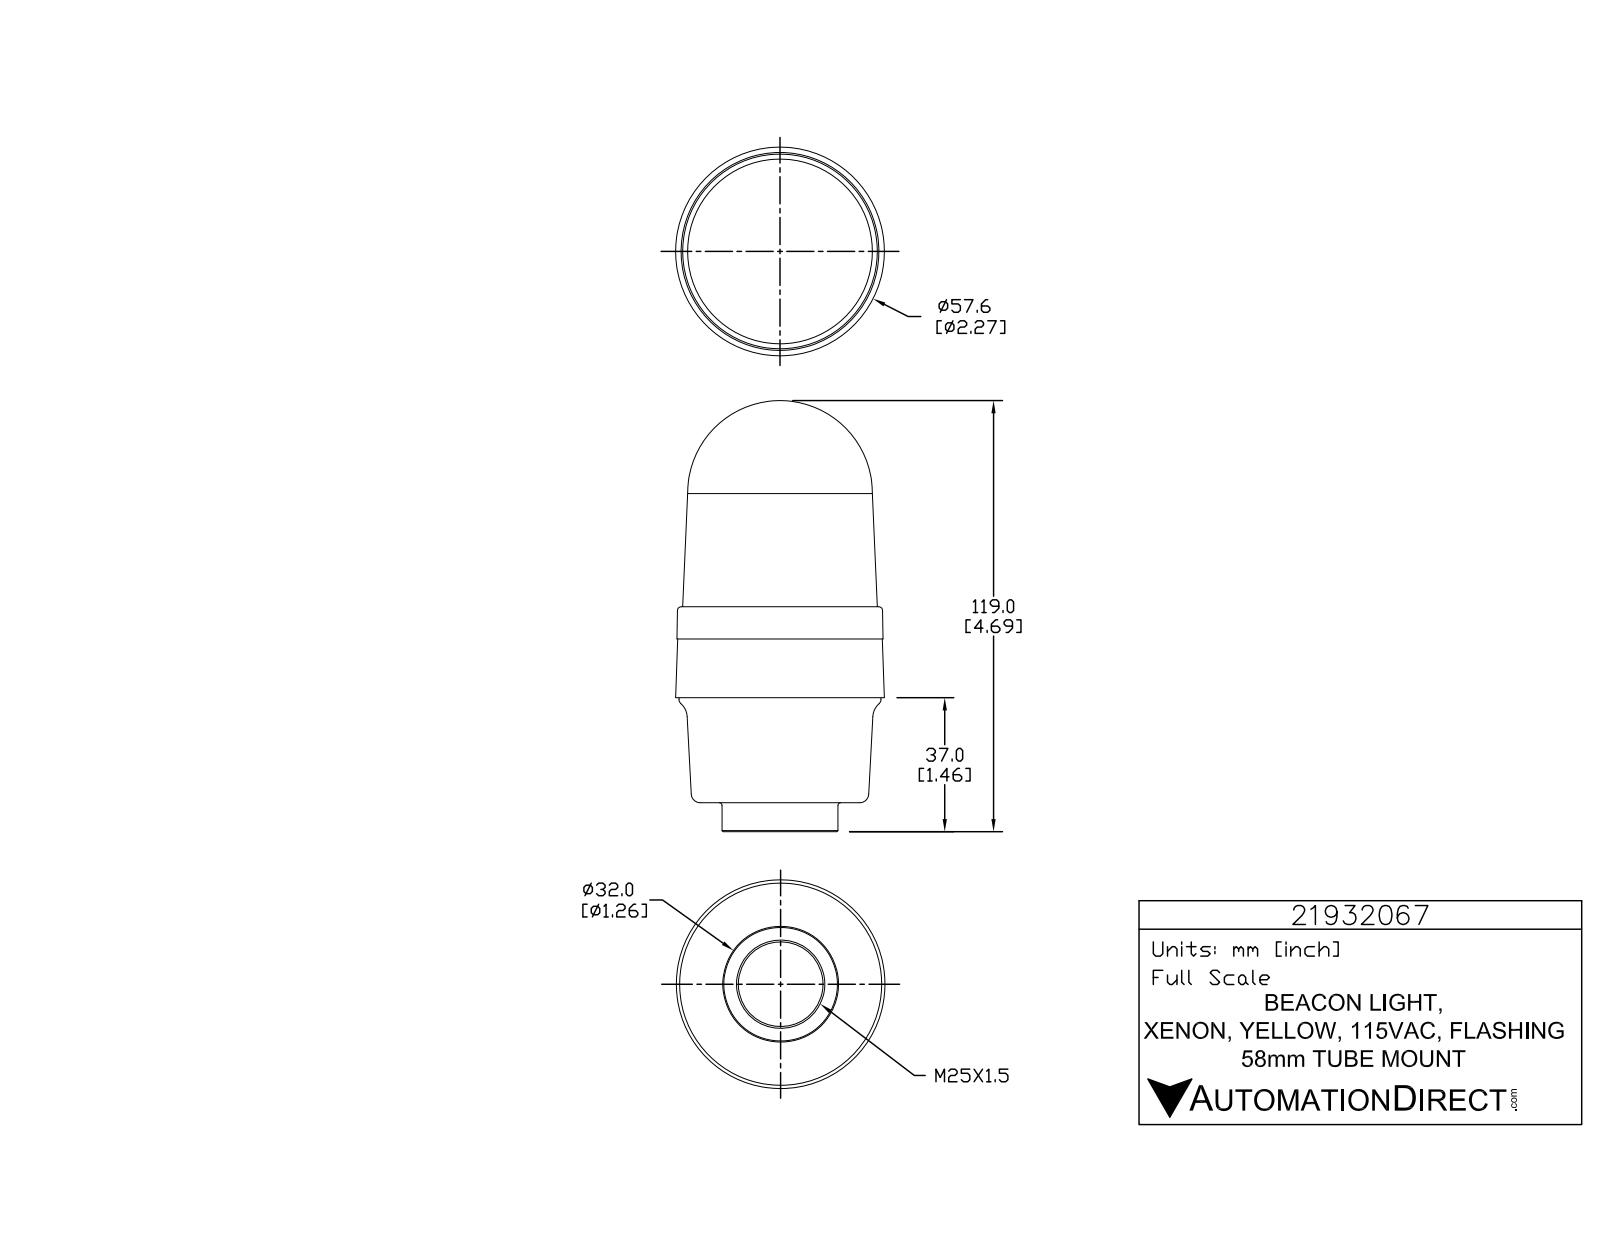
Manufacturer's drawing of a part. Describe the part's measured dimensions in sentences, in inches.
The part is named "21932067". Its 3-D file was written by "SolidWorks 2015 (AUTOMOTIVE_DESIGN)". It is 1 solid with 791 faces: 525 planar, 168 cylindrical and 98 other. Overall it measures 4.685 by 2.269 by 2.269 inches. Its volume is 13.89 cubic inches and its surface area 34.06 square inches. Round holes: 3 of diameter 0.039, 1 of diameter 0.92. Round bosses or shafts: 3 of diameter 0.226, 3 of diameter 0.056, 1 of diameter 2.197, 1 of diameter 1.26. Partial cylindrical surfaces (rounded edges, fillets, slot ends): 6 of radius 0.008, 6 of radius 0.008, 6 of radius 0.008, 6 of radius 0.131, 3 of radius 0.004, 3 of radius 0.005, 3 of radius 0.008, 3 of radius 0.008. The main face-to-face distances are 0.315, 1.142, 1.457, 0.988, 2.13, 2.445, 0.35, 0.638, 1.78, 2.094.
